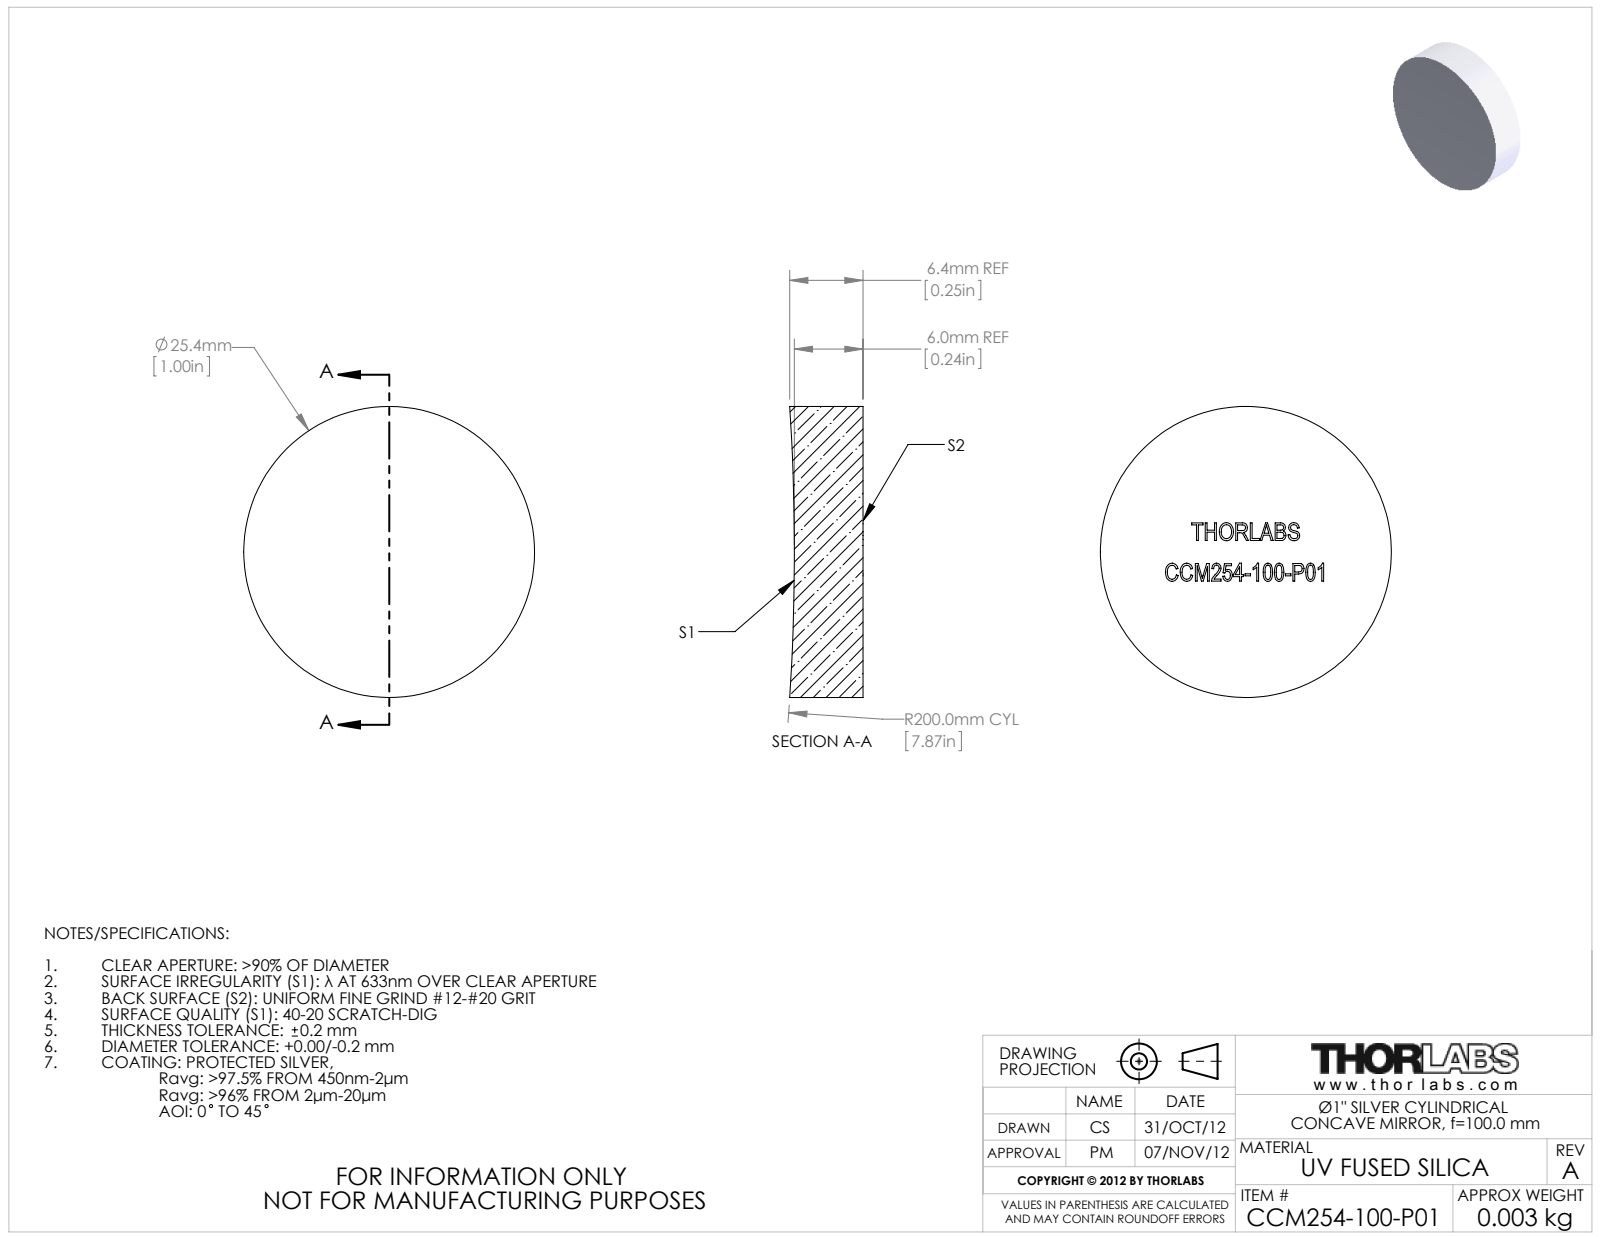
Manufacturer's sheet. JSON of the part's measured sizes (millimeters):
{"part_name": "TTN005968-E0W", "step_written_by": "SolidWorks 2012 (CONFIG_CONTROL_DESIGN)", "units": "millimeters", "bodies": {"solids": 1, "faces": 37, "planar": 33, "cylindrical": 4, "other": 0}, "overall_size": [25.4, 25.4, 6.4], "volume_mm3": 3091, "surface_area_mm2": 1509, "round_bosses_or_shafts": [[25.4, 1]], "partial_cylinders_radius": [[200, 1]]}
